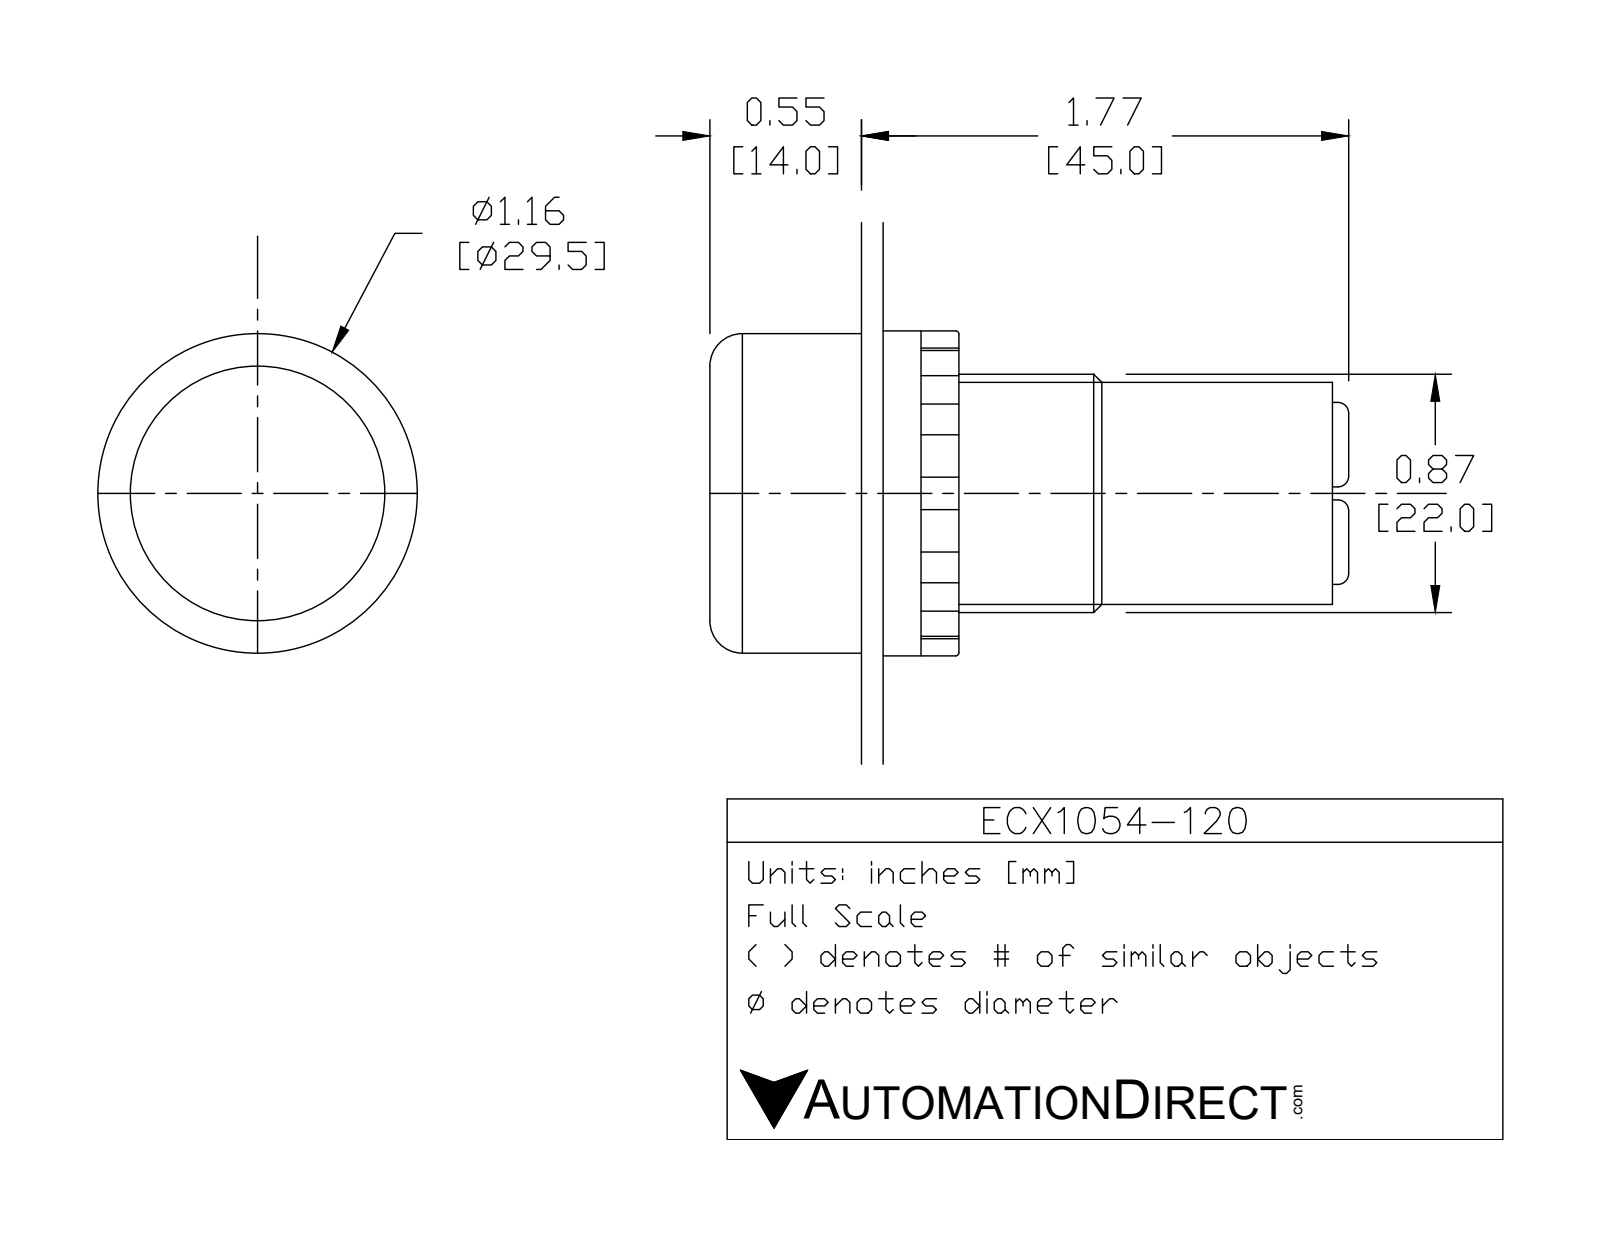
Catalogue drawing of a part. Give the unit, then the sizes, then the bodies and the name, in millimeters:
Units: millimetres
Overall size (bounding box): 59 × 30 × 30
Round holes (diameter × count): ⌀5.5 ×2, ⌀22.5 ×1
Round bosses / shafts (diameter × count): ⌀4 ×2, ⌀30 ×1, ⌀29 ×1, ⌀26.5 ×1, ⌀22 ×1, ⌀20 ×1
Partial cylindrical surfaces — rounded edges, fillets, slot ends (radius × count): R1 ×12, R9 ×1
Main face-to-face distances: 13.5, 0.5, 14, 20, 6, 6.5, 39, 7, 13, 27
Hole centre spacings: 4.62, 9.24
Volume: 26 294 mm³ · Surface area: 9 700 mm²
Bodies: 6 solids, 125 faces (63 planar, 41 cylindrical, 21 other)
Part name (STEP PRODUCT): ECX1054-120
STEP written by: SolidWorks 2017 (AUTOMOTIVE_DESIGN)
